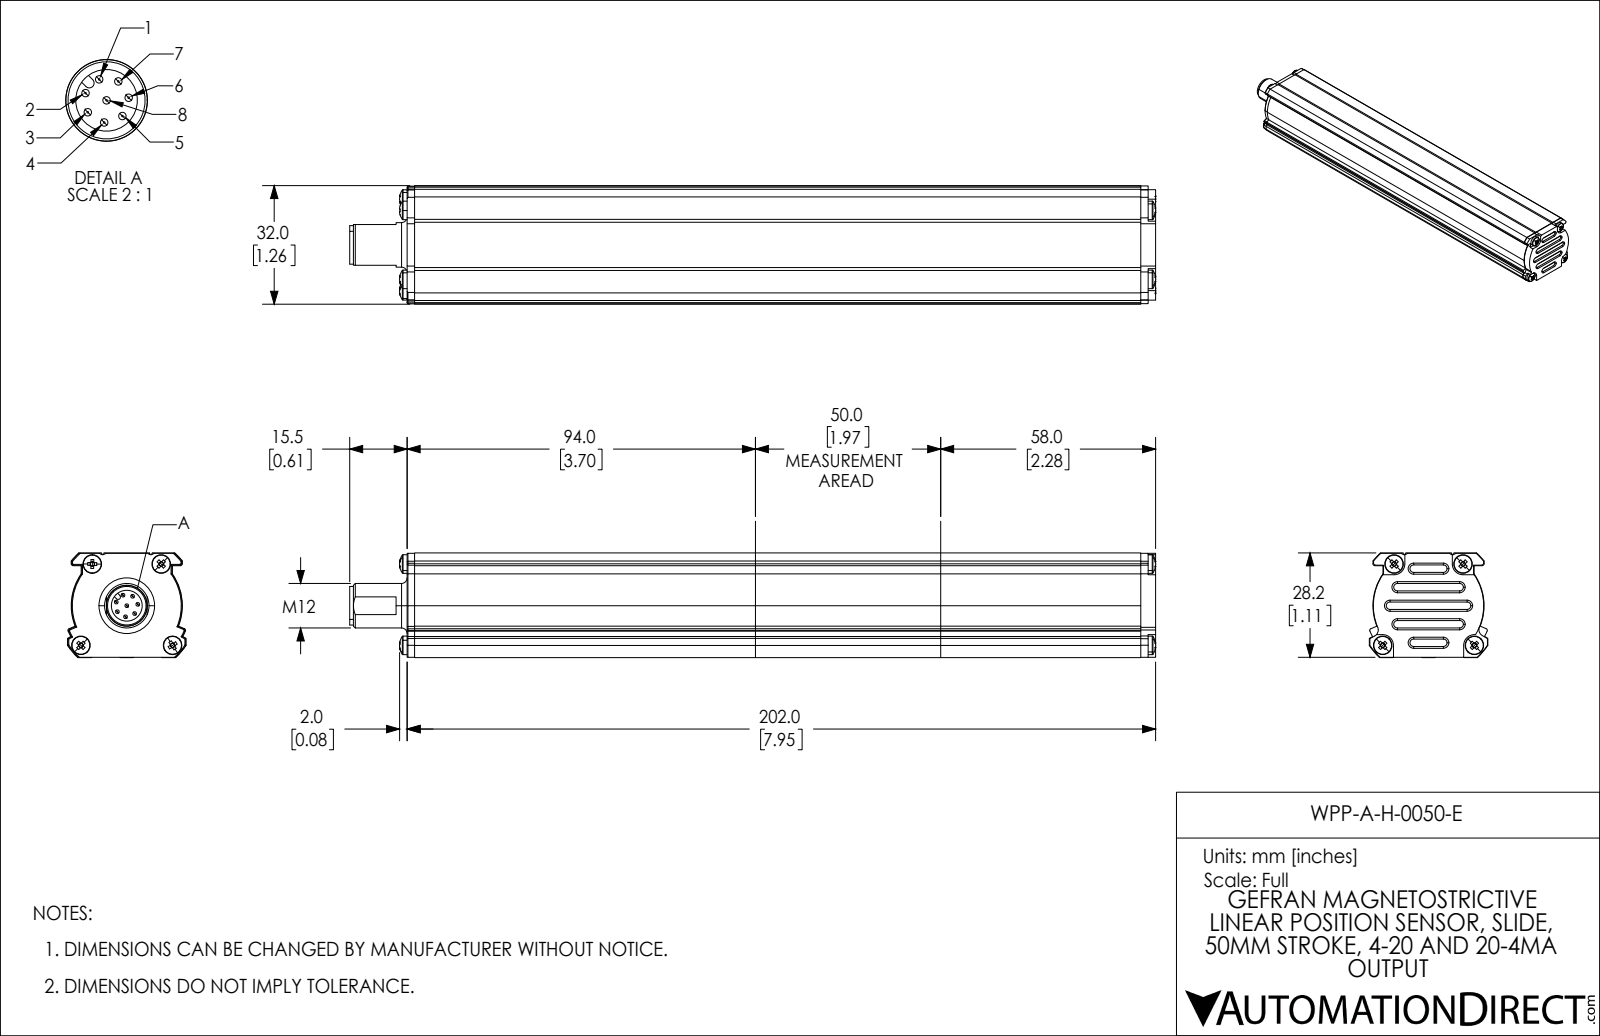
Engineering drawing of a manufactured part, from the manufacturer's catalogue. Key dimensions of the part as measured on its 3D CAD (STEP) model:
Part name (STEP PRODUCT): WPP-A-H-0050-E
STEP written by: SolidWorks 2021 (CONFIG_CONTROL_DESIGN)
Units: millimetres
Bodies: 20 solids, 605 faces (301 planar, 131 cylindrical, 173 other)
Overall size (bounding box): 217.55 × 32 × 28.25
Volume: 161 704 mm³ · Surface area: 38 324 mm²
Round holes (diameter × count): ⌀2.6 ×5, ⌀2.3 ×4, ⌀7 ×1, ⌀8.3 ×1, ⌀9.4 ×1
Round bosses / shafts (diameter × count): ⌀1 ×8, ⌀5 ×4, ⌀12 ×1, ⌀10.4 ×1, ⌀9.55 ×1, ⌀8 ×1
Partial cylindrical surfaces — rounded edges, fillets, slot ends (radius × count): R0.5 ×8, R2.9 ×4, R0.4 ×2, R1 ×2, R1.85 ×2, R0.65 ×1, R2 ×1, R14.9 ×1
Main face-to-face distances: 28, 28.25, 196, 2, 198, 24.8, 24.55, 3.45, 3.7, 28.3
Hole centre spacings: 16.36, 14.6, 22.17, 30.85, 18.6, 22.16, 24.75, 24.76
